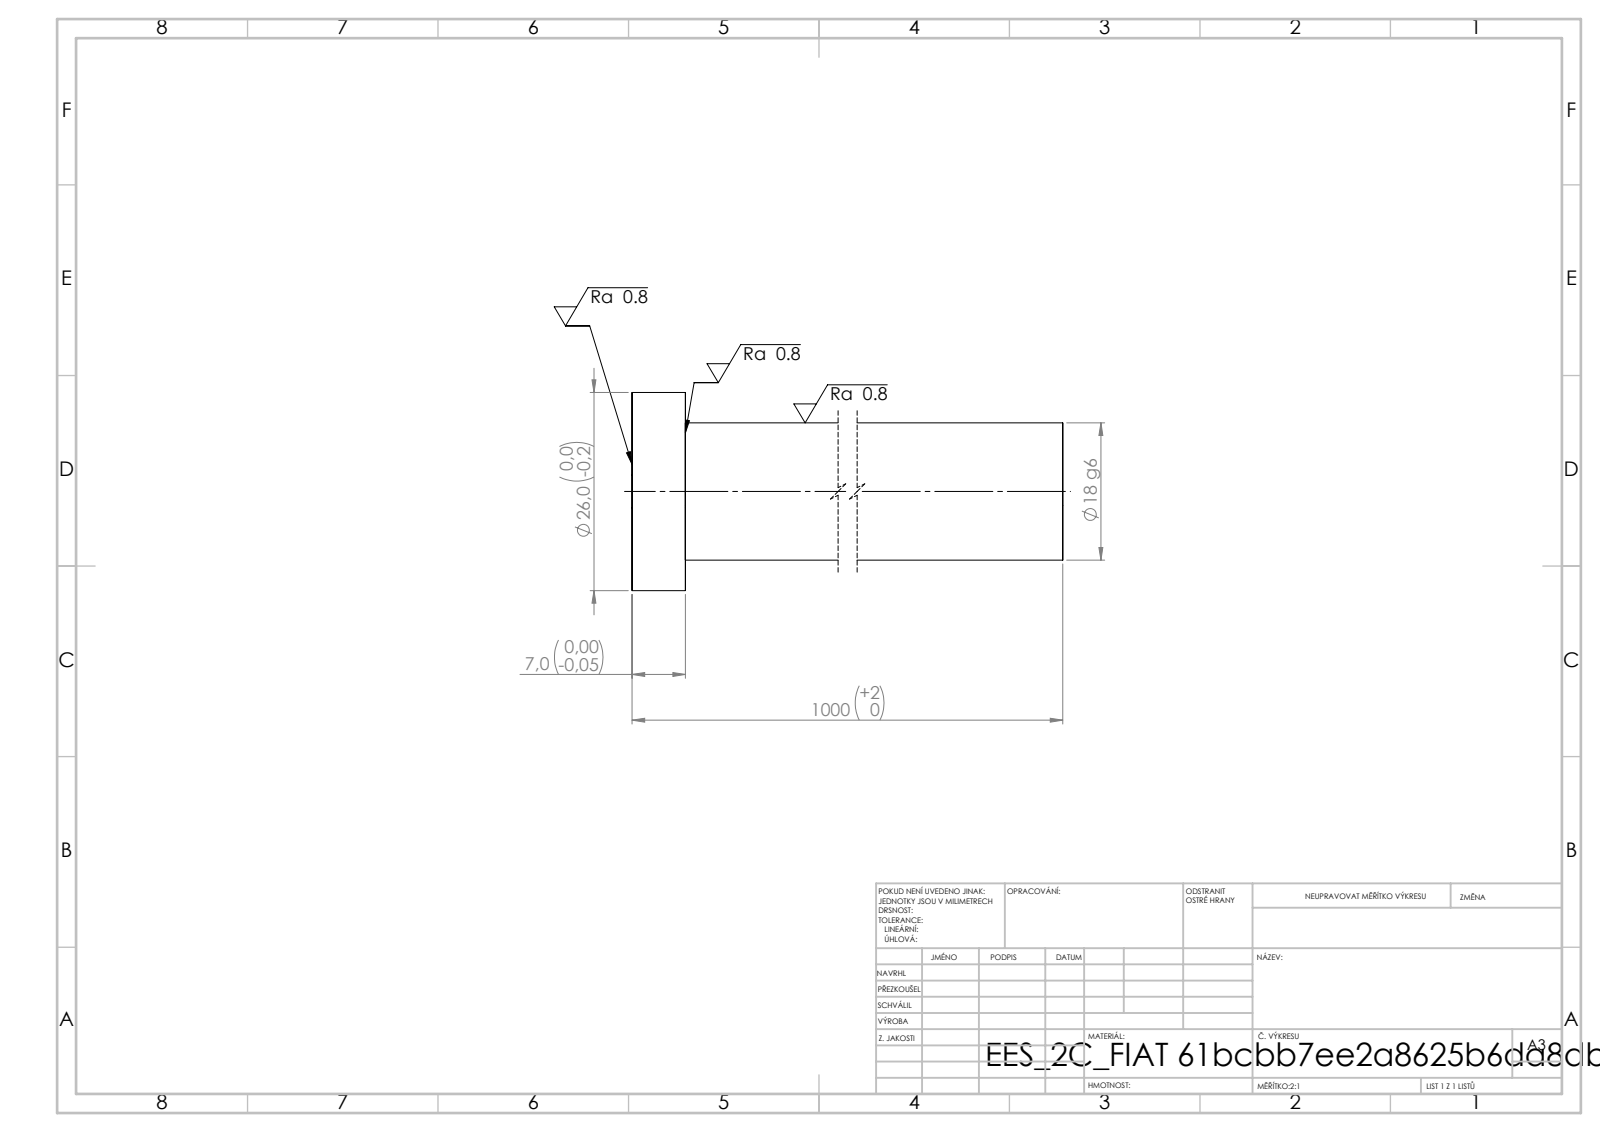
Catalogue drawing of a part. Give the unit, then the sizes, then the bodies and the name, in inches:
Units: inches
Overall size (bounding box): 39.37 × 1.024 × 1.024
Round bosses / shafts (diameter × count): ⌀1.024 ×1, ⌀0.709 ×1
Main face-to-face distances: 0.276, 39.37, 39.094
Volume: 15.65 in³ · Surface area: 89.57 in²
Bodies: 1 solid, 7 faces (3 planar, 4 cylindrical, 0 other)
STEP written by: SolidWorks 2019 (CONFIG_CONTROL_DESIGN)
